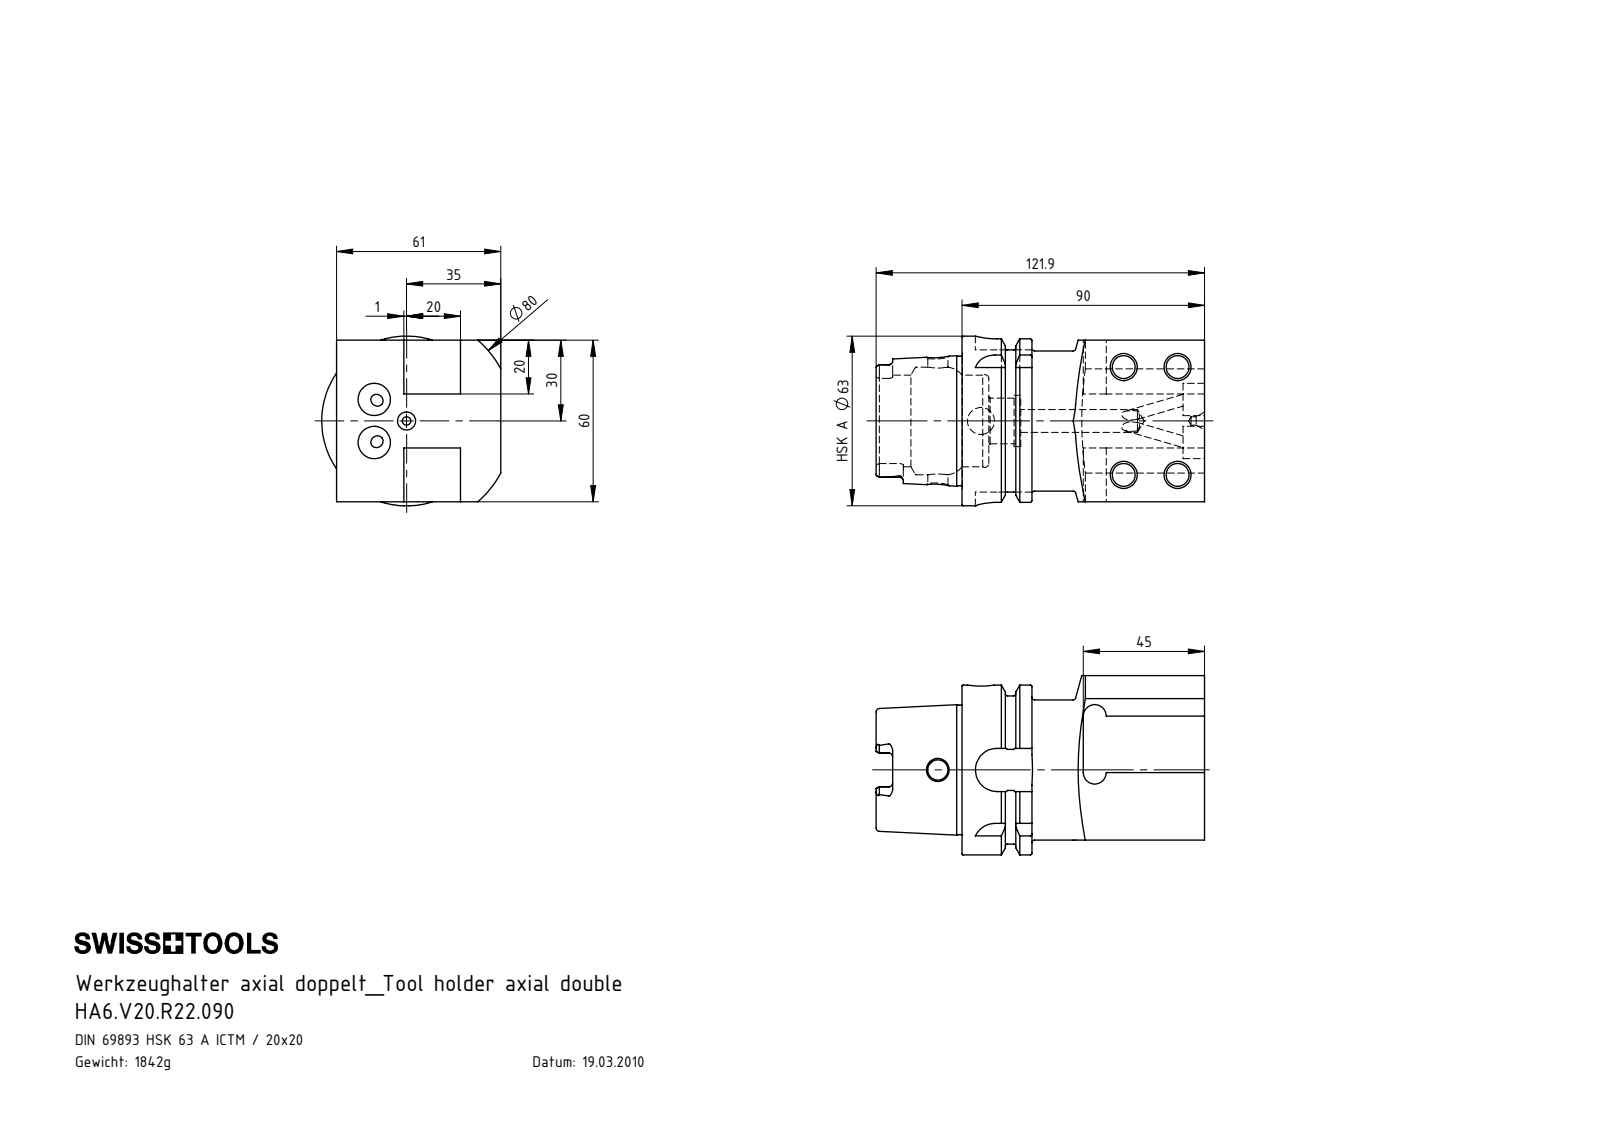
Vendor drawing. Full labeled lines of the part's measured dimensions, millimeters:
Part name (STEP PRODUCT): KU1-U12.001.010_2; ISO 4026 - M10 x 25; KU1-U12.001.010; HA6.V20.R22.090 (+2 more)
STEP written by: SolidWorks 2022 (CONFIG_CONTROL_DESIGN)
Units: millimetres
Bodies: 9 solids, 304 faces (99 planar, 89 cylindrical, 116 other)
Overall size (bounding box): 123.7 × 66.5 × 63
Volume: 243 150 mm³ · Surface area: 52 763 mm²
Round holes (diameter × count): ⌀4.2 ×4, ⌀8.5 ×4, ⌀7 ×2, ⌀12 ×2, ⌀3.15 ×1, ⌀7.5 ×1, ⌀8.4 ×1, ⌀10 ×1, ⌀17 ×1, ⌀19 ×1, ⌀34 ×1, ⌀40 ×1
Round bosses / shafts (diameter × count): ⌀10 ×4, ⌀63 ×1, ⌀54.95 ×1, ⌀52 ×1, ⌀47.94 ×1
Partial cylindrical surfaces — rounded edges, fillets, slot ends (radius × count): R1.4 ×6, R2.88 ×4, R8 ×4, R4.5 ×2, R40 ×1
Main face-to-face distances: 20, 40, 45, 61, 60, 15, 46, 25, 21, 36
Hole centre spacings: 14.42, 20, 40, 44.72, 56.65, 75.69, 16
